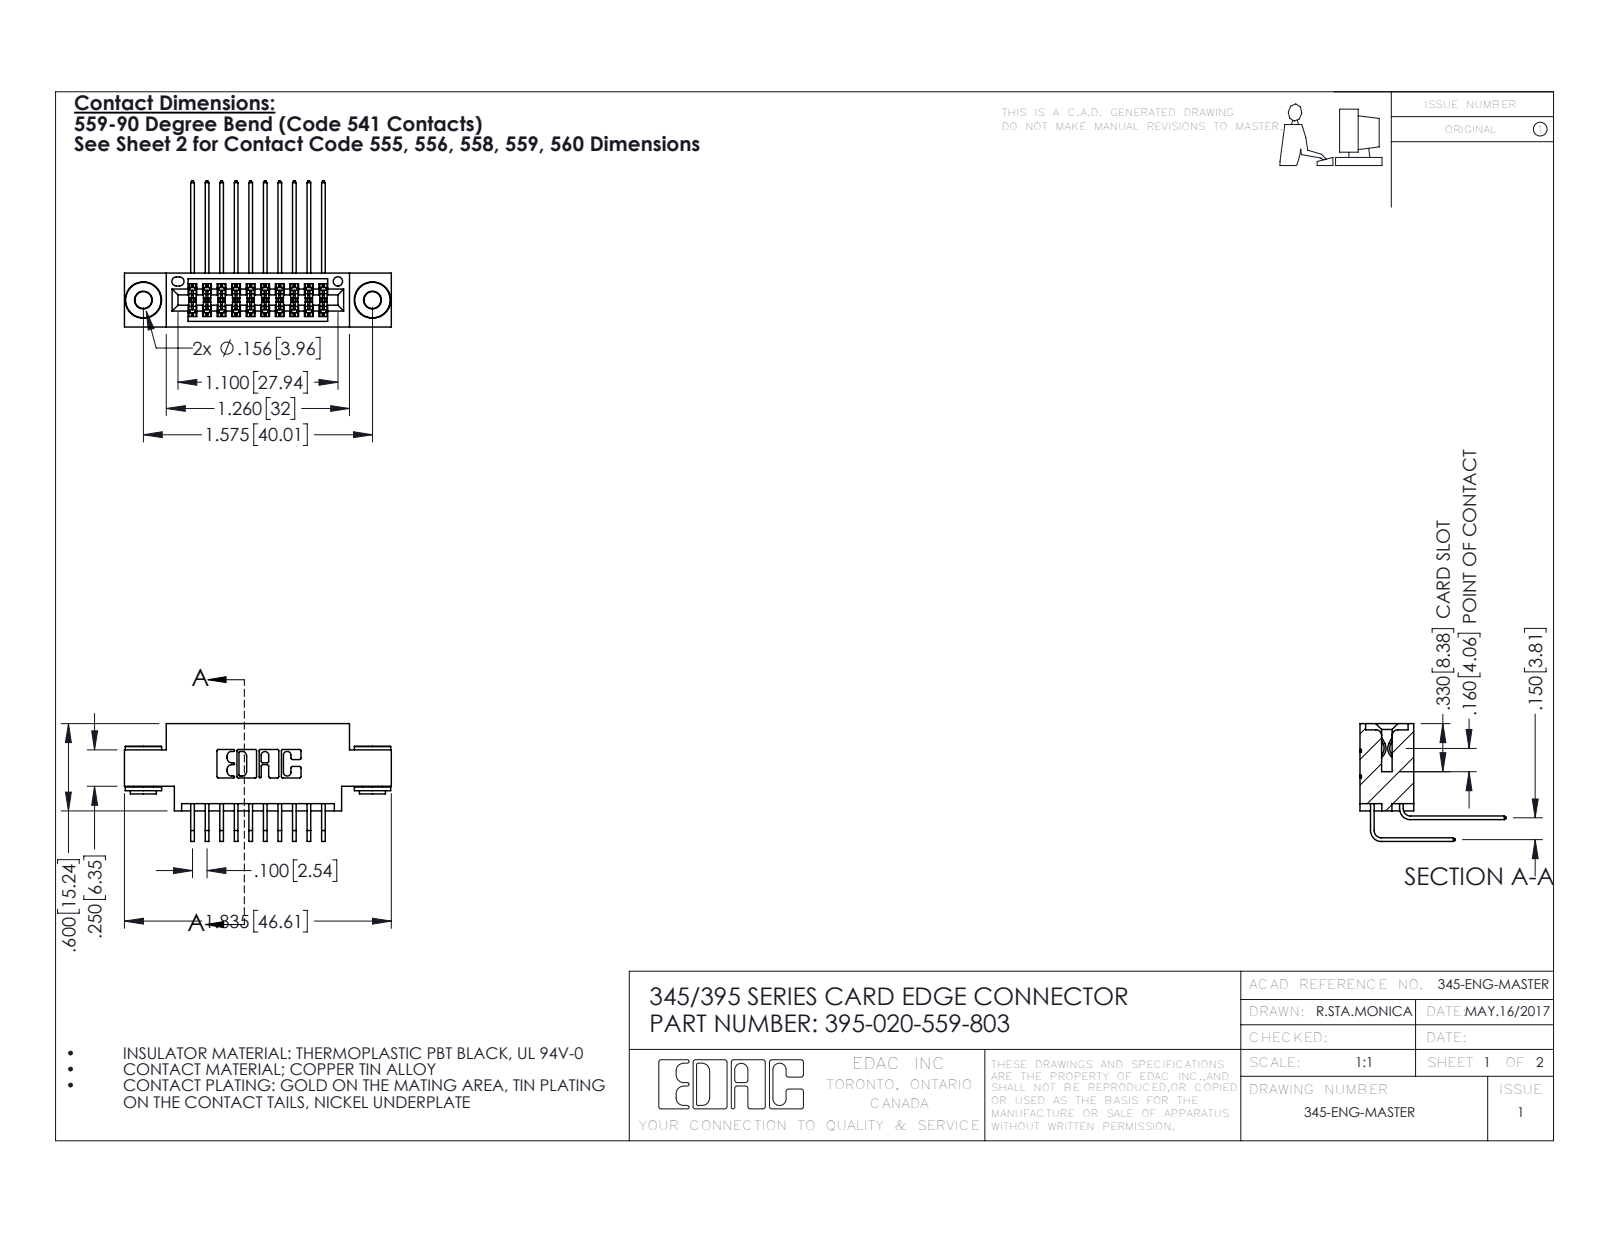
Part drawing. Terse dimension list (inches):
name: 345 Part_0.170 Offset - 0.156 Dia-TH; 345-250-002_345-250-002-102; 345-292-001_558 559 Tail - 1; 395-020-559-803 (+1 more)
written by: SolidWorks 2016 (CONFIG_CONTROL_DESIGN)
unit: in
bodies: 23 solids, 1208 faces (794 planar, 406 cylindrical, 8 other)
size: 1.835 × 1.005 × 0.809
volume: 0.259 in³; area: 10.16 in²
holes: 2× ⌀0.116, 2× ⌀0.156, 1× ⌀0.064
bosses: 2× ⌀0.25, 2× ⌀0.18, 2× ⌀0.136
rounds: 31× R0.006, 22× R0.01, 6× R0.007, 6× R0.031, 3× R0.026, 2× R0.014, 2× R0.019, 2× R0.022
face distances: 0.37, 0.072, 0.298, 0.2, 0.175, 0.098, 0.272, 0.025, 0.15, 0.1
hole spacings: 0.27, 1.344, 1.575
